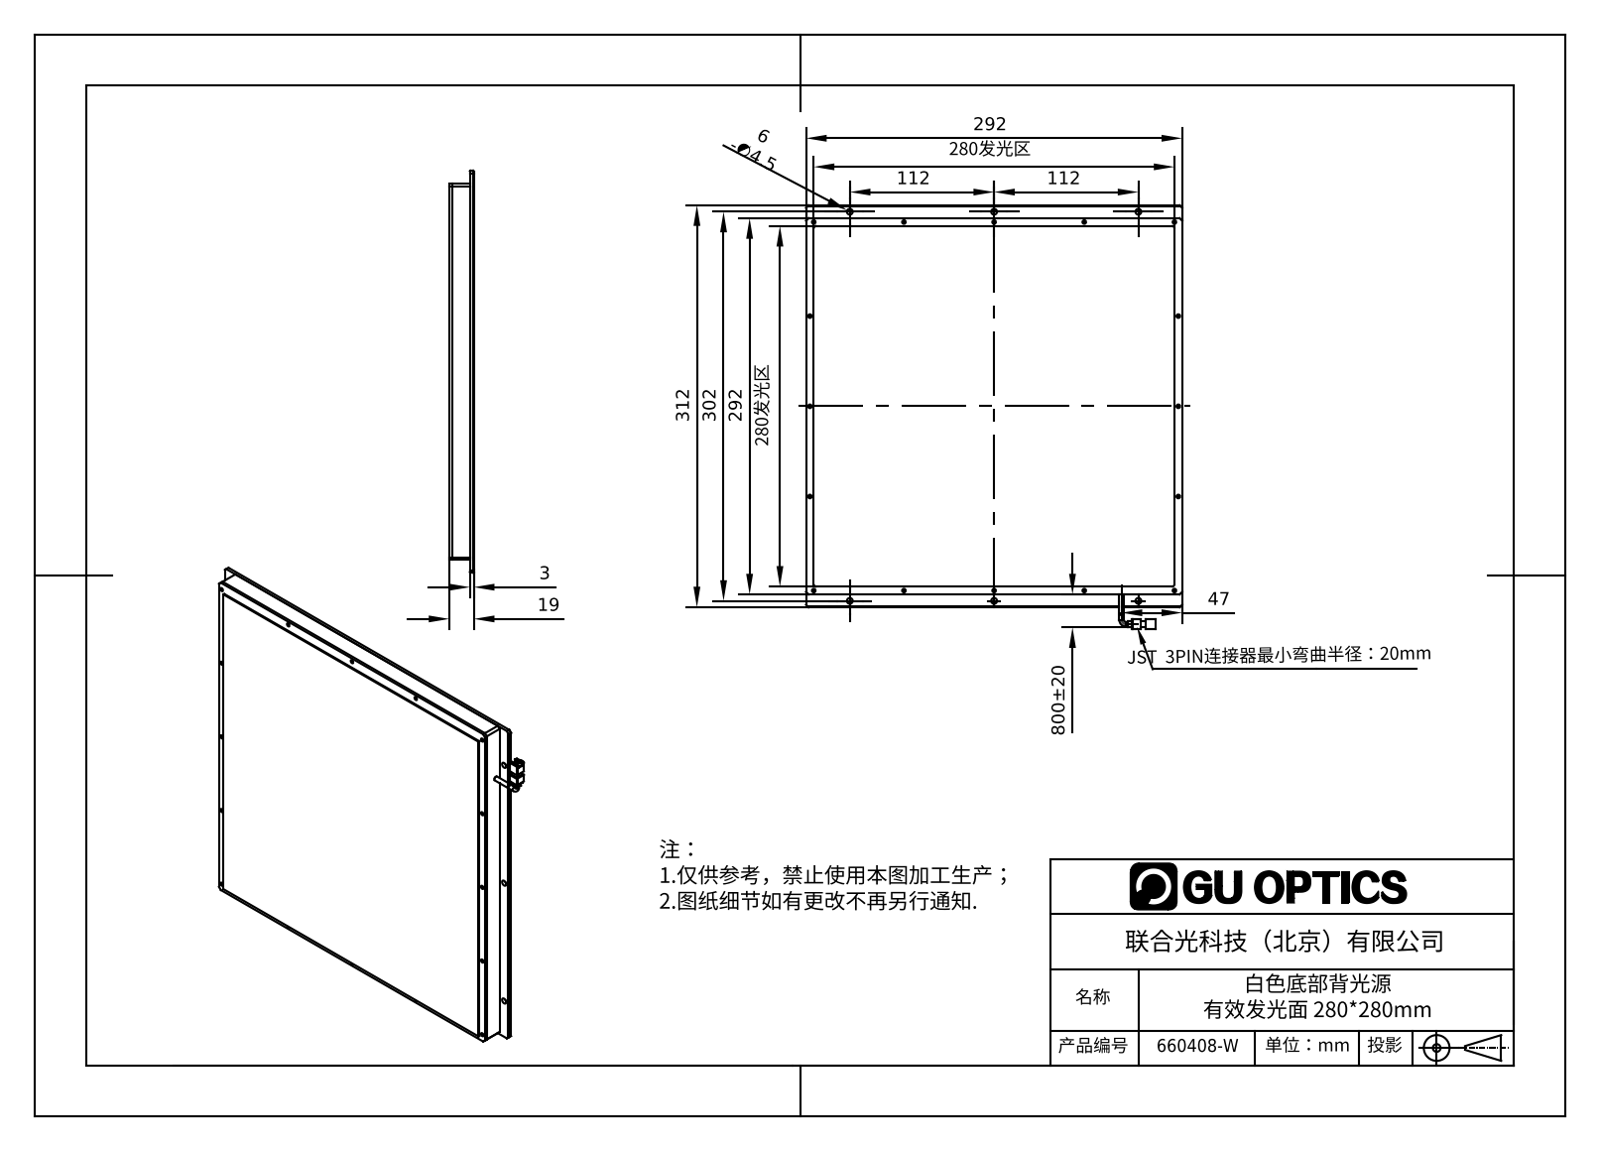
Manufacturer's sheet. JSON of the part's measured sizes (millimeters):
{"part_name": "660408-W", "step_written_by": "SolidWorks 2016 (AUTOMOTIVE_DESIGN)", "units": "millimeters", "bodies": {"solids": 5, "faces": 539, "planar": 169, "cylindrical": 270, "other": 100}, "overall_size": [329, 292, 20], "volume_mm3": 614608, "surface_area_mm2": 407504, "round_holes": [[1.6, 32], [1.25, 16], [1.5, 16], [2, 16], [2.4, 16], [2.8, 16], [4.5, 6]], "round_bosses_or_shafts": [[3.5, 2]], "partial_cylinders_radius": [[0.5, 8], [1, 8], [2, 6]], "face_to_face_distances": [17, 3, 14, 20, 6, 286, 292, 16, 1, 280], "hole_center_spacings": [286, 70, 294.44, 80, 210, 296.98, 140, 160.56]}
